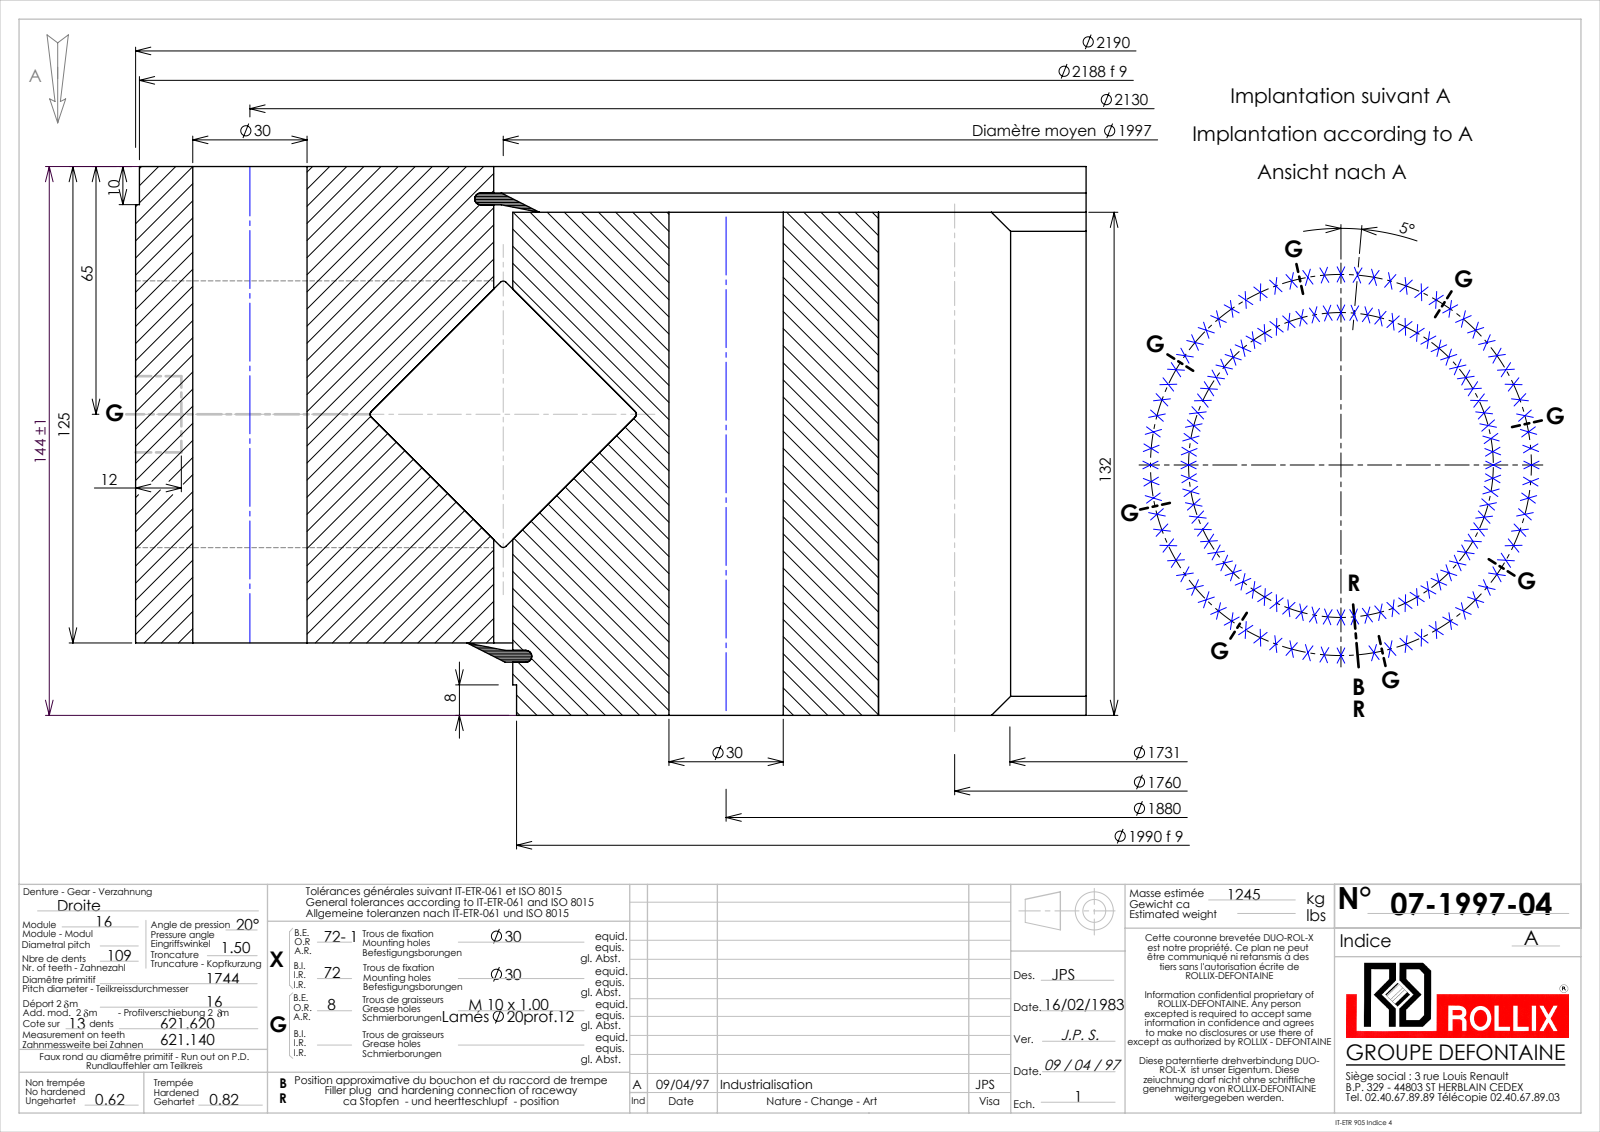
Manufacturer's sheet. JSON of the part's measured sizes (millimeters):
{"part_name": "07-1997-04", "step_written_by": "SolidWorks 2016 (CONFIG_CONTROL_DESIGN)", "units": "millimeters", "bodies": {"solids": 5, "faces": 1063, "planar": 242, "cylindrical": 557, "other": 264}, "overall_size": [2190, 2190, 144], "volume_mm3": 140100000, "surface_area_mm2": 8933000, "round_holes": [[30, 143], [9, 8], [20, 8], [2002, 1]], "round_bosses_or_shafts": [[2190, 1], [2188, 1], [1992, 1], [1990, 1], [50, 1]], "partial_cylinders_radius": [[865.5, 1], [900, 1]], "face_to_face_distances": [132, 19, 113, 144, 125, 12, 1.95, 114.95, 3.1, 5.05], "hole_center_spacings": [163.85, 245.39, 82, 326.46, 486.58, 794.52, 565.33, 940]}
